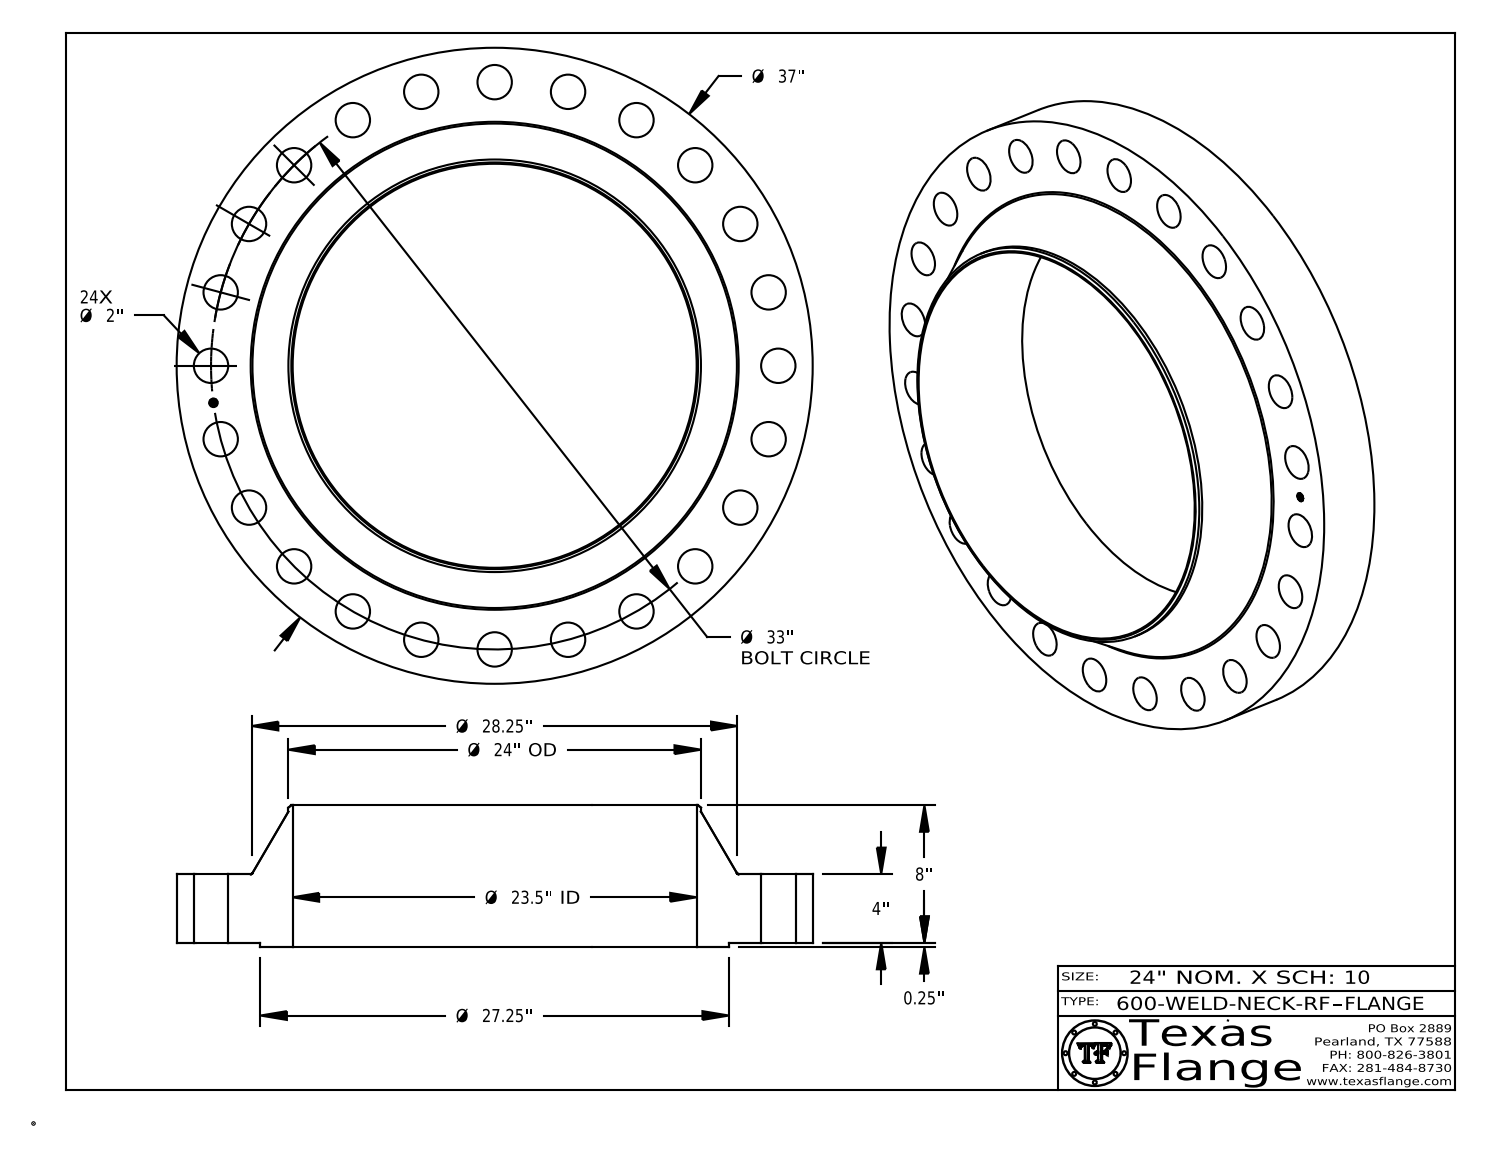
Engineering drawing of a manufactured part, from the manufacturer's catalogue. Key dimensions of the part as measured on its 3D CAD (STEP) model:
Part name (STEP PRODUCT): 600-WELD-NECK-RF
STEP written by: CATIA V5 STEP AP214 (AUTOMOTIVE_DESIGN)
Units: inches
Bodies: 1 solid, 451 faces (369 planar, 76 cylindrical, 6 other)
Overall size (bounding box): 37 × 37 × 8.25
Volume: 2 684 in³ · Surface area: 3 022 in²
Round holes (diameter × count): ⌀2 ×24, ⌀0.495 ×1, ⌀23.5 ×1
Round bosses / shafts (diameter × count): ⌀0.03 ×8, ⌀37 ×1, ⌀27.25 ×1, ⌀24 ×1, ⌀0.39 ×1
Main face-to-face distances: 4, 0.25, 4.25, 8.25, 8, 0.015, 4.235, 3.985, 4.015, 0.07
Hole centre spacings: 16.5, 4.307, 8.541, 20.089, 23.335, 26.181, 31.876, 32.718
